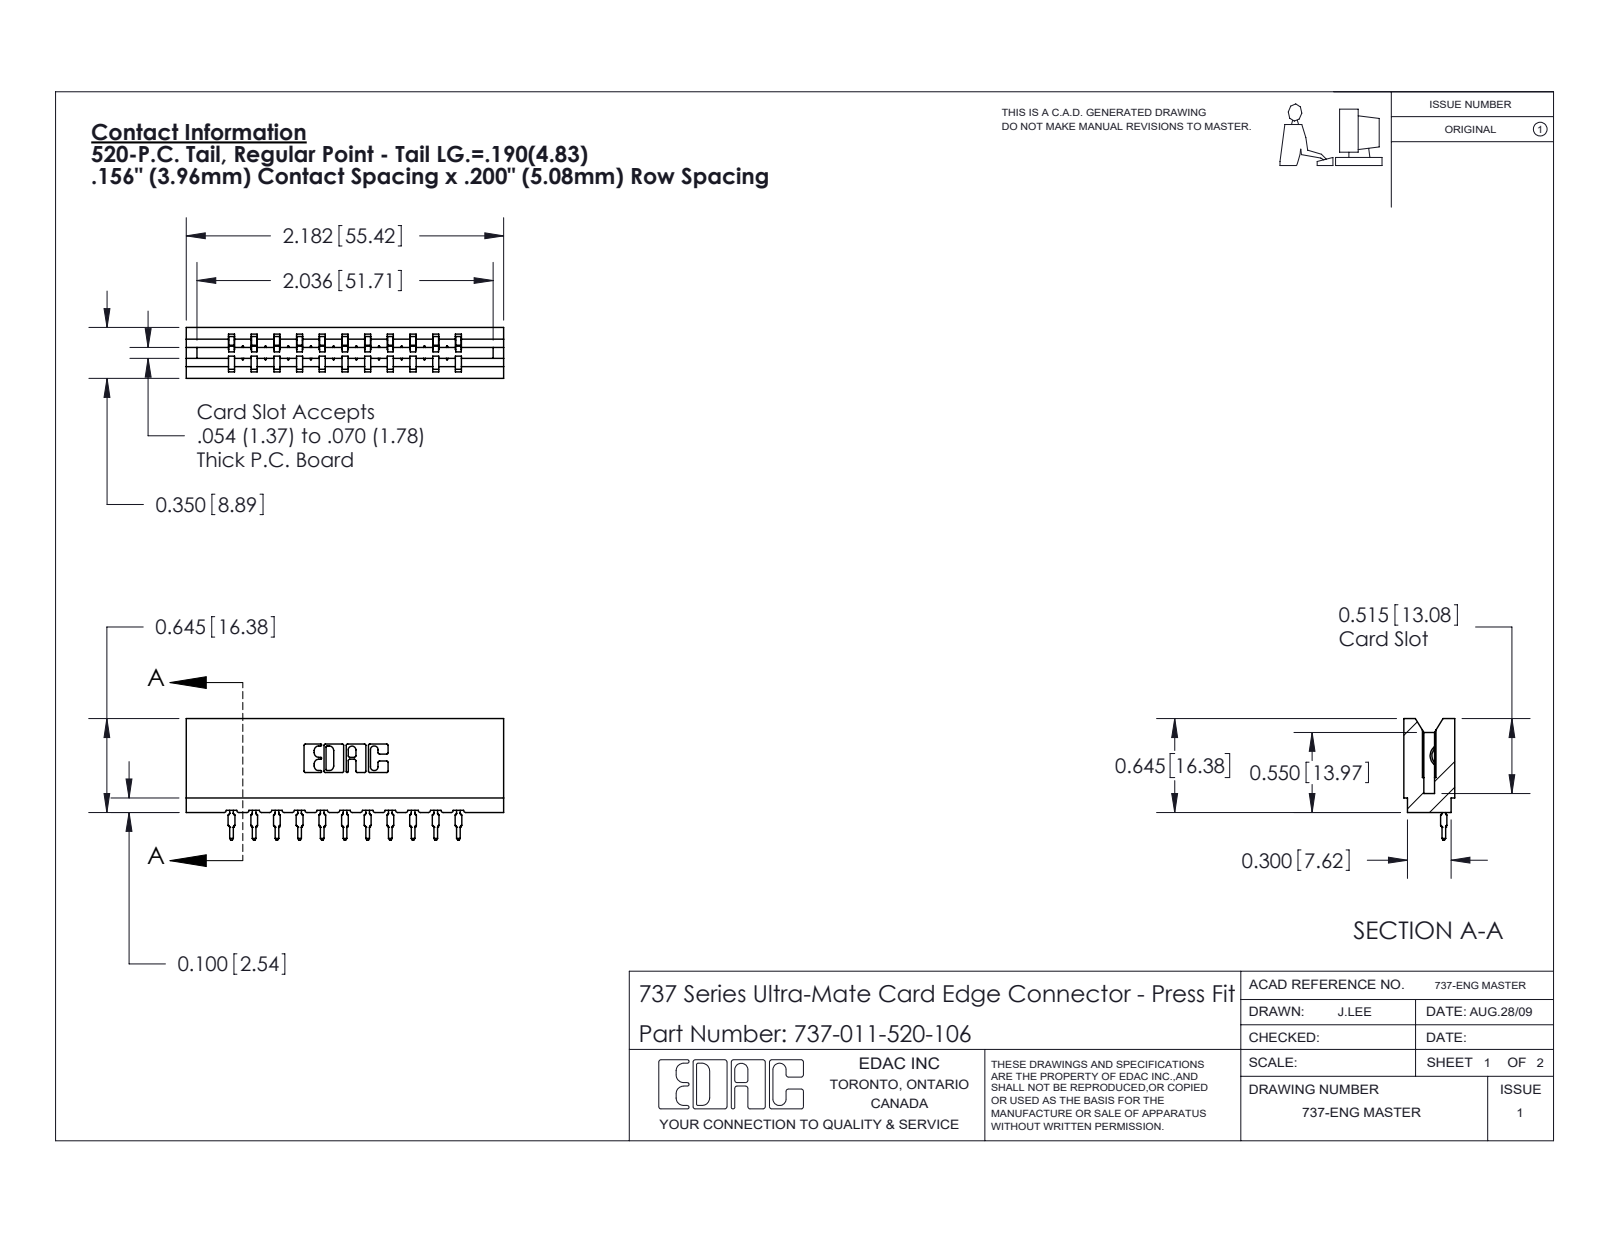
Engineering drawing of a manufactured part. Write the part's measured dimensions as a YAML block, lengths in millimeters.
part_name: "737-011-520-106; 737 Part_Insulator Option - 06; 745-292-001_520"
step_written_by: "SolidWorks 2020 (CONFIG_CONTROL_DESIGN)"
units: millimeters
bodies: {solids: 12, faces: 1338, planar: 803, cylindrical: 249, other: 286}
overall_size: [55.4, 21.2, 8.9]
volume: 5540
surface_area: 6800
partial_cylinders:
  - {radius: 0.3, count: 22}
  - {radius: 0.4, count: 22}
  - {radius: 0.5, count: 22}
  - {radius: 0.2, count: 6}
  - {radius: 0.8, count: 6}
  - {radius: 0.1, count: 4}
  - {radius: 0.3, count: 4}
  - {radius: 0.7, count: 3}
face_to_face_distances: [4, 3.5, 5.4, 8.9, 15.8, 9, 7.9, 19.8, 11.9, 1.9]
